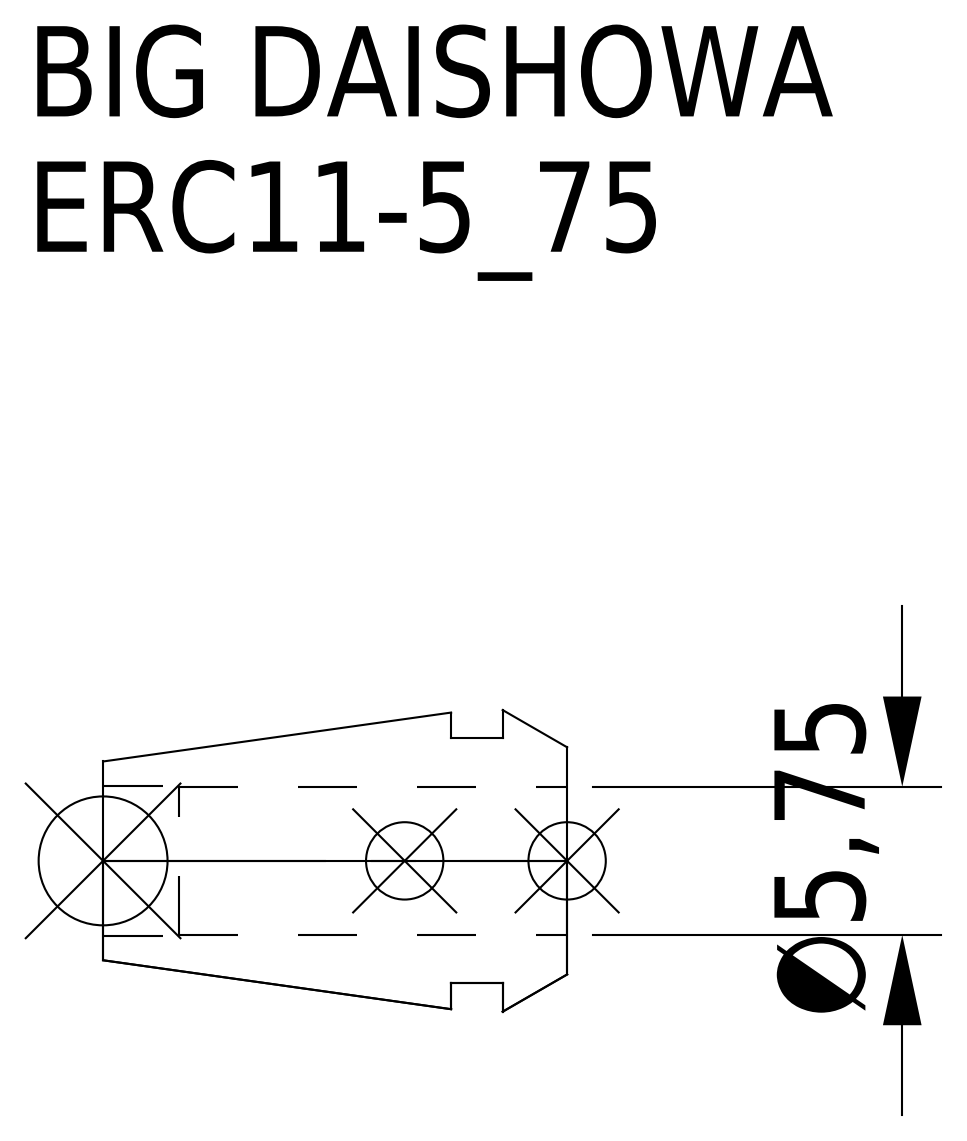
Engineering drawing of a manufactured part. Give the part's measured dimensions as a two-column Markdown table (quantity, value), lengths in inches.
| quantity | value |
| --- | --- |
| part name | ERC11-5_75 |
| STEP written by | CREO PARAMETRIC BY PTC INC, 2016380 (AUTOMOTIVE_DESIGN) |
| units | inches |
| bodies | 1 solid, 15 faces (5 planar, 6 cylindrical, 4 other) |
| overall size | 0.709 × 0.461 × 0.461 |
| volume | 0.053 in³ |
| surface area | 1.573 in² |
| round holes (diameter × count) | 0.226 × 1, 0.228 × 1 |
| round bosses / shafts (diameter × count) | 0.374 × 1 |
| main face-to-face distances | 0.098, 0.177, 0.079, 0.709, 0.61, 0.531, 0.593, 0.495, 0.416, 0.115 |
